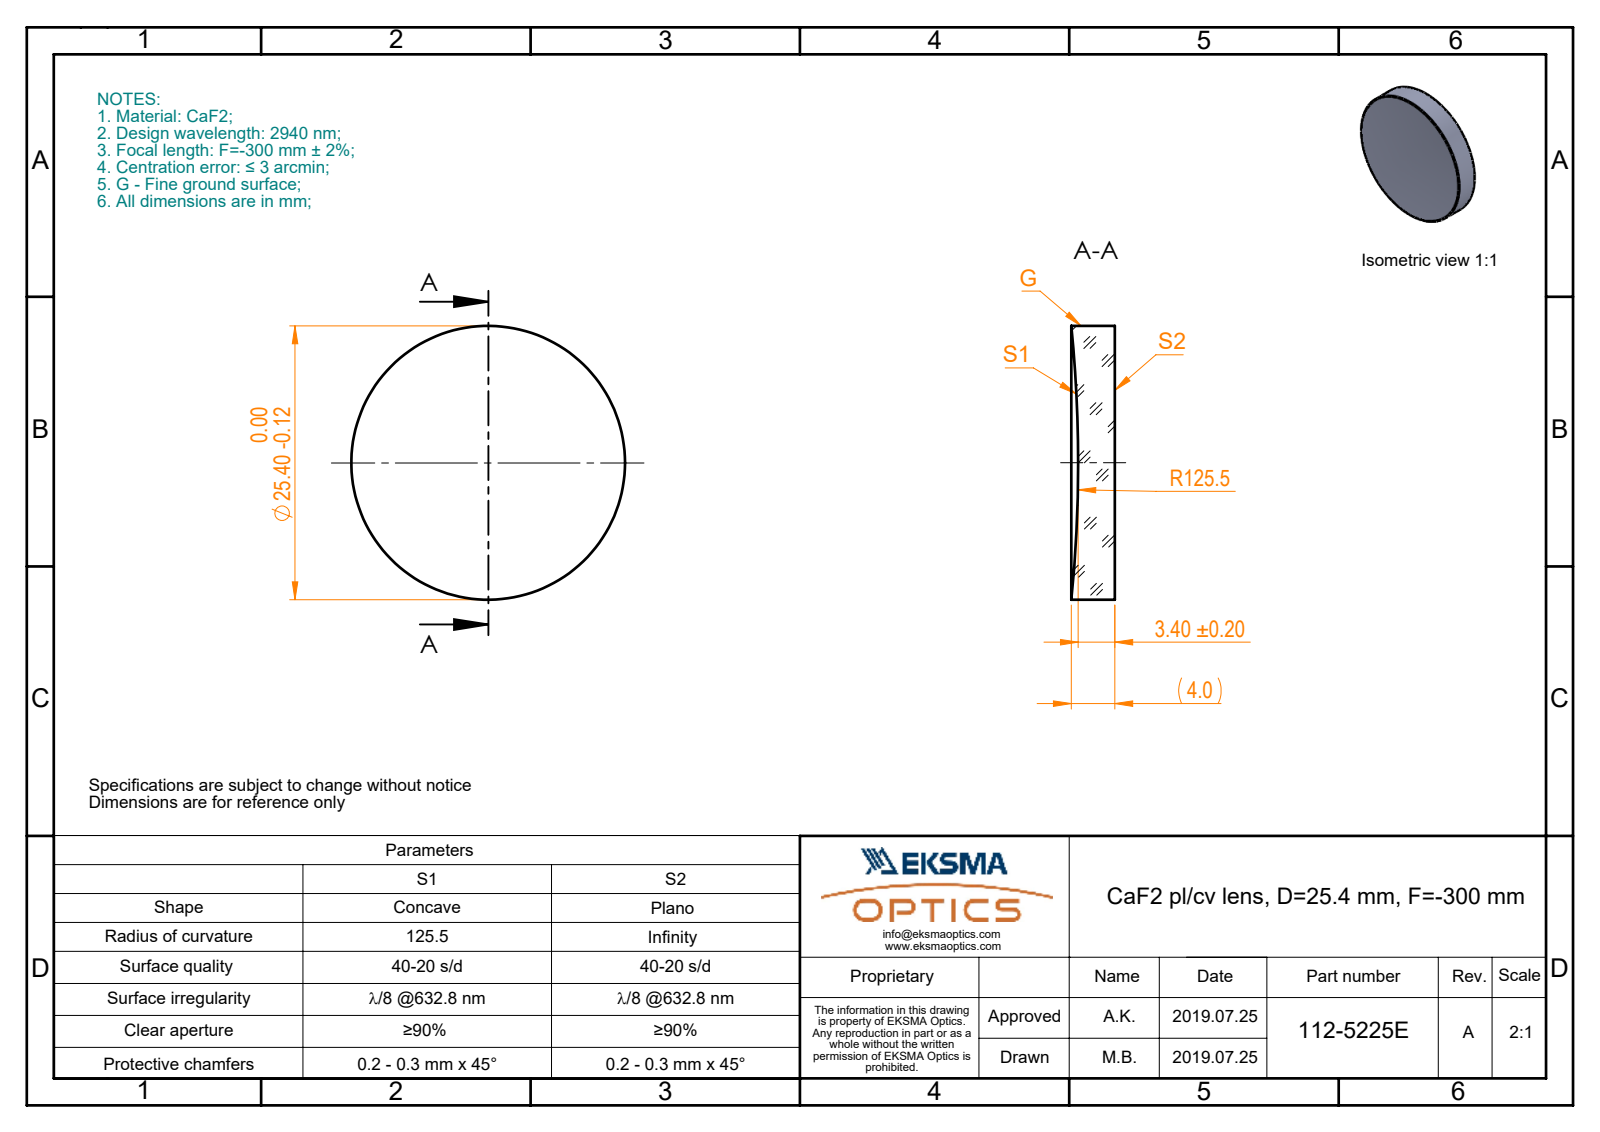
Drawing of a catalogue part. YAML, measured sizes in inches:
part_name: "112-5225E CaF2 pl-cv 25.4 F-300"
step_written_by: "SolidWorks 2017 (CONFIG_CONTROL_DESIGN)"
units: inches
bodies: {solids: 1, faces: 5, planar: 1, cylindrical: 2, other: 2}
overall_size: [1, 1, 0.159]
volume: 0.115
surface_area: 2.072
round_bosses_or_shafts:
  - {diameter: 1, count: 1}
